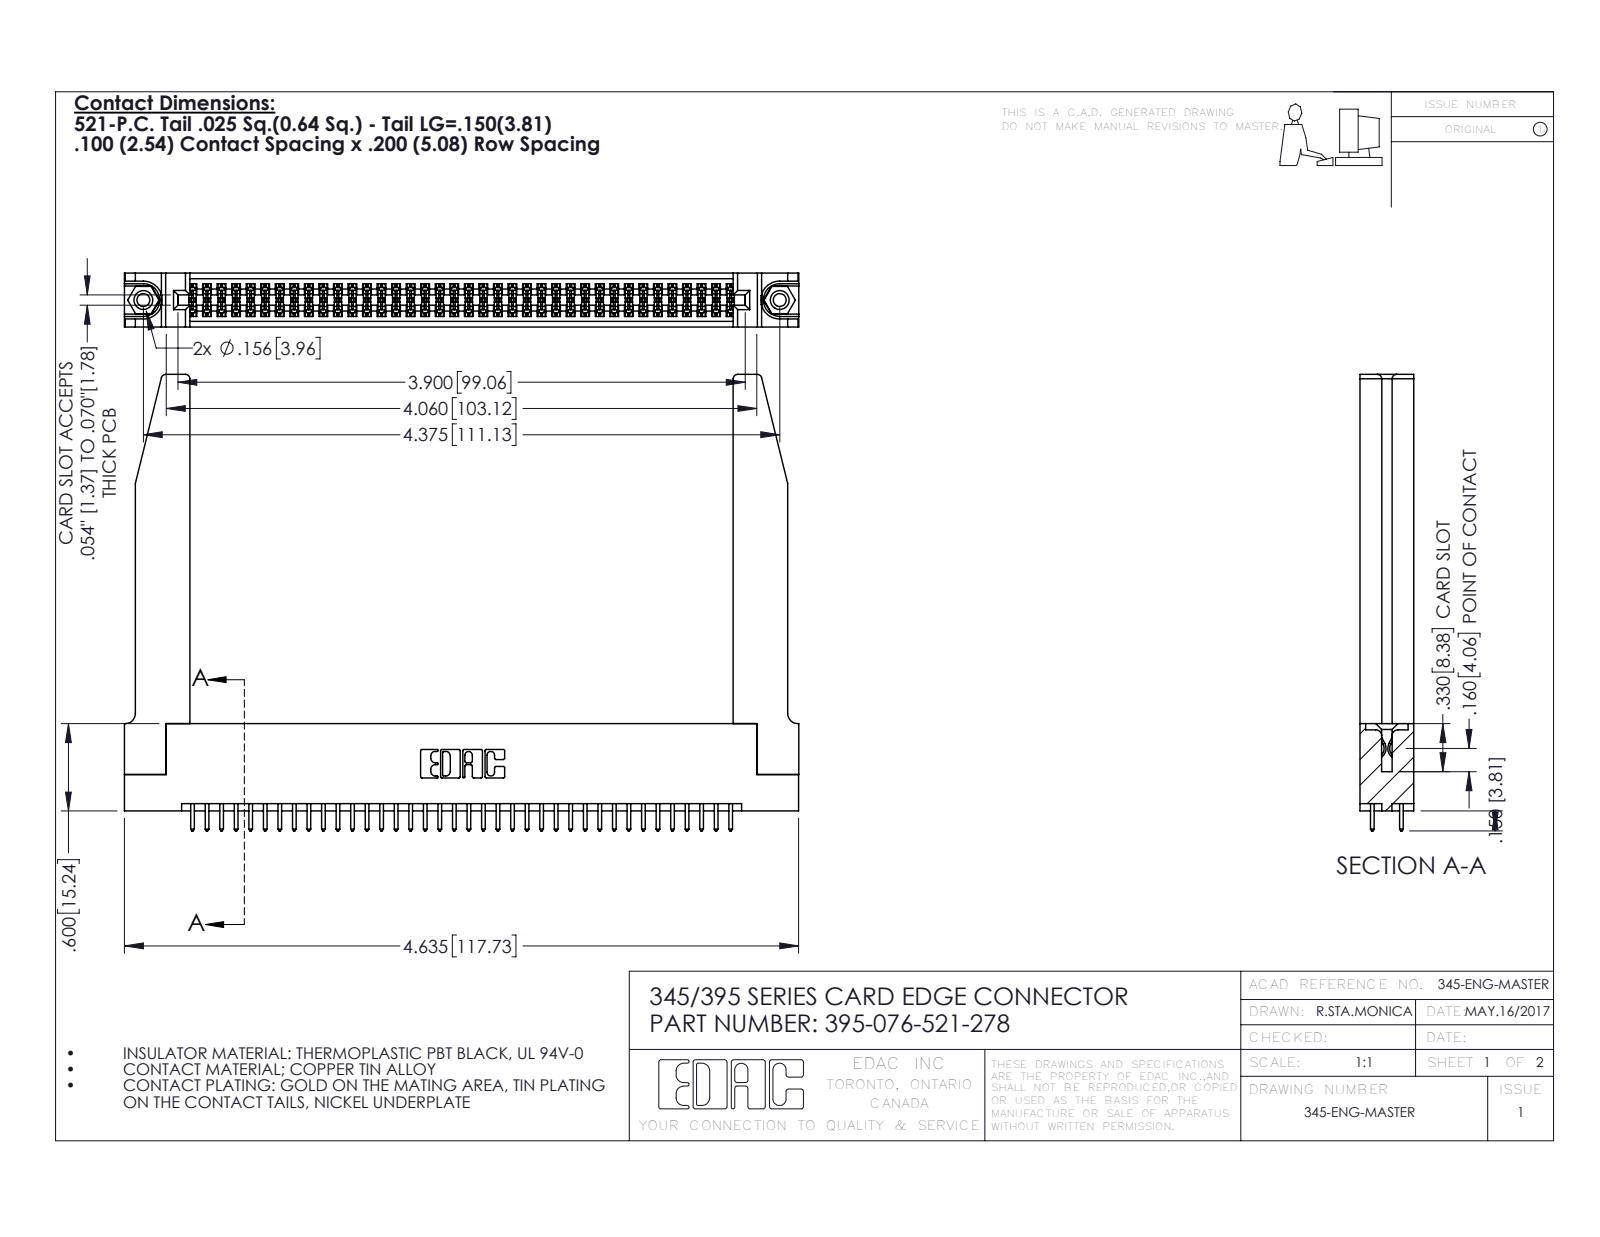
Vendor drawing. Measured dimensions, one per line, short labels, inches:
name: 345 Part_Flush Mounting Lugs - 0.156 Dia-TH; 345-250-001_345-250-001-102; 395-076-521-278; 345-220-078_345-220-078 (+1 more)
written by: SolidWorks 2016 (CONFIG_CONTROL_DESIGN)
unit: in
bodies: 81 solids, 4160 faces (2730 planar, 1378 cylindrical, 52 other)
size: 4.636 × 3.137 × 0.37
volume: 1.168 in³; area: 36.22 in²
holes: 2× ⌀0.089, 2× ⌀0.125, 2× ⌀0.156, 1× ⌀0.064
bosses: 2× ⌀0.155
rounds: 114× R0.006, 76× R0.01, 22× R0.01, 8× R0.03, 6× R0.007, 6× R0.031, 3× R0.026, 2× R0.014
face distances: 0.37, 0.072, 0.298, 0.2, 0.098, 0.272, 0.025, 0.225, 0.148, 0.15
hole spacings: 0.27, 4.139, 4.375
